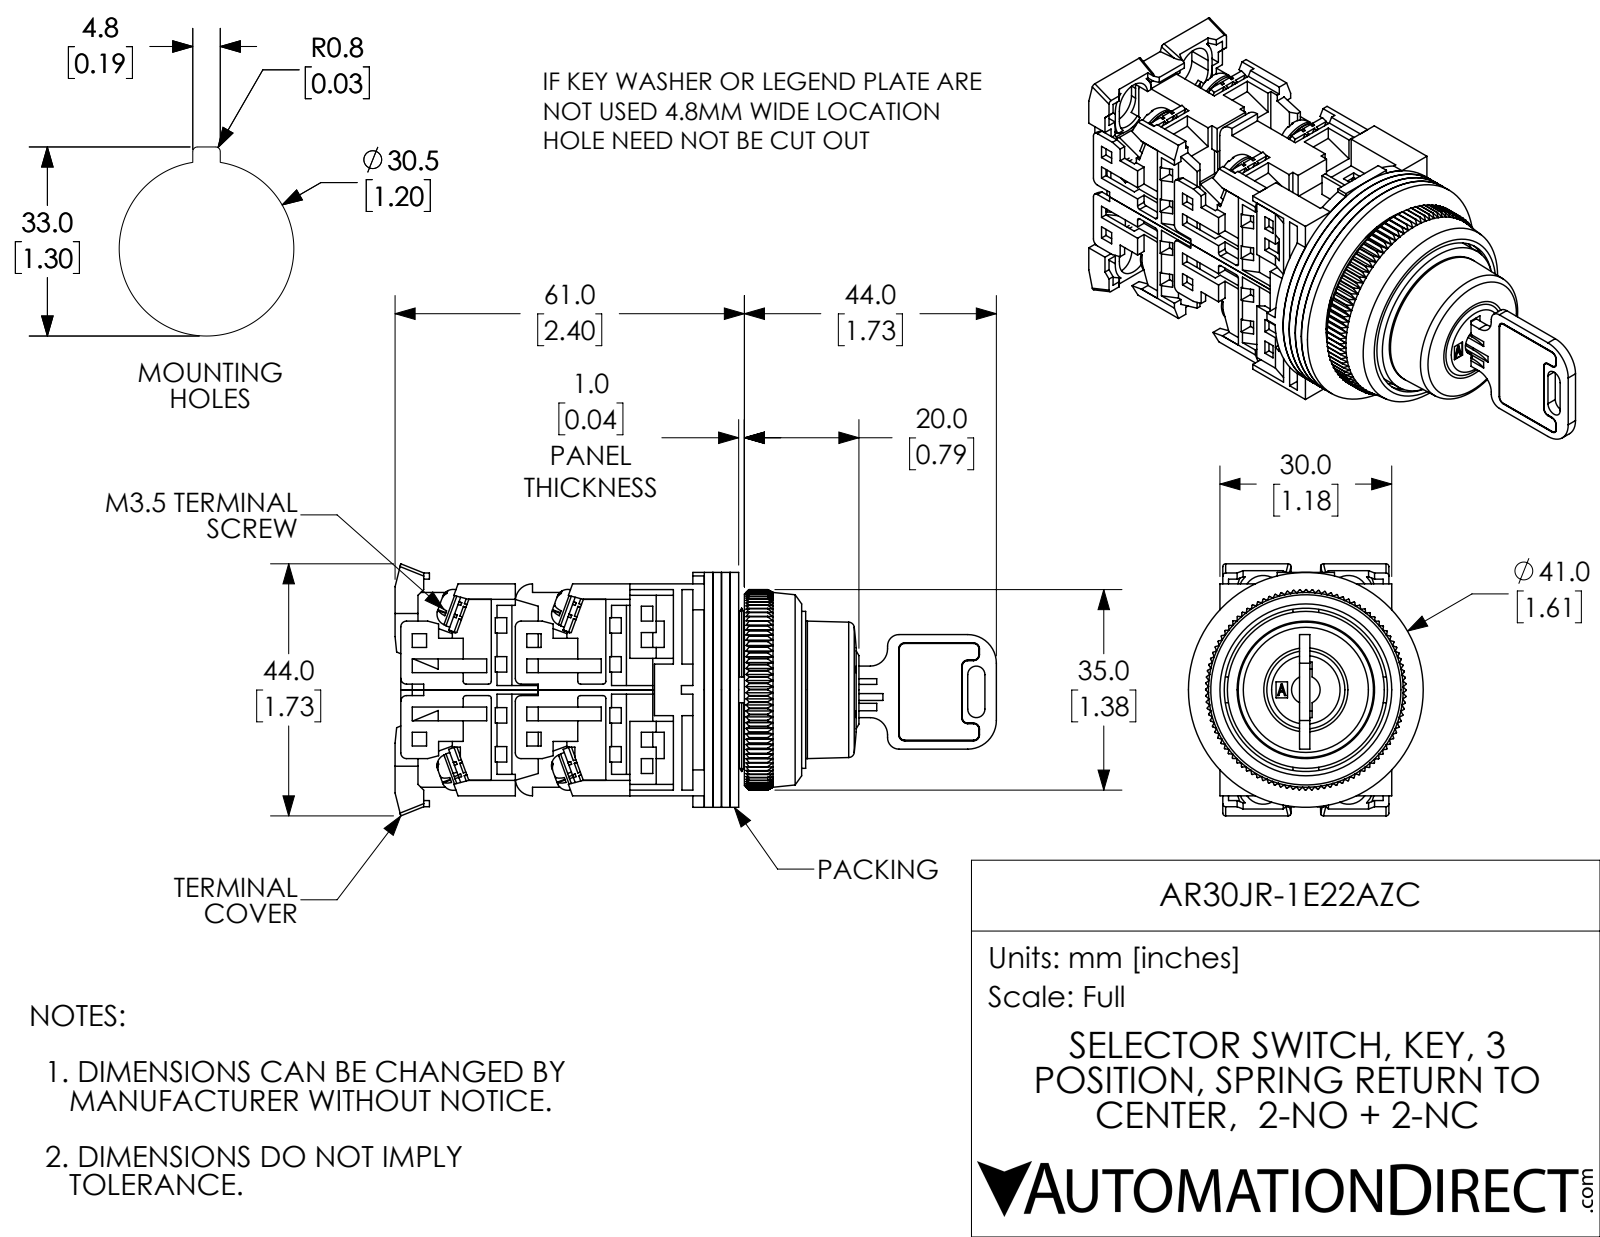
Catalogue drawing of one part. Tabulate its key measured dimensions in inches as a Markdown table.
| quantity | value |
| --- | --- |
| part name | AR30JR-1E22AZC |
| STEP written by | SolidWorks 2017 (AUTOMOTIVE_DESIGN) |
| units | inches |
| bodies | 38 solids, 2546 faces (1941 planar, 325 cylindrical, 280 other) |
| overall size | 4.134 × 1.732 × 1.614 |
| volume | 3.32 in³ |
| surface area | 69.28 in² |
| round holes (diameter × count) | 0.138 × 12, 0.142 × 8, 0.118 × 1, 0.709 × 1, 0.945 × 1, 1.122 × 1, 1.181 × 1, 1.252 × 1 |
| round bosses / shafts (diameter × count) | 0.26 × 8, 0.138 × 8, 1.614 × 1, 1.15 × 1, 1.079 × 1 |
| partial cylindrical surfaces (radius × count) | 0.059 × 34, 0.02 × 16, 0.039 × 9, 0.118 × 6, 0.008 × 4, 0.138 × 4, 0.177 × 4, 0.079 × 2 |
| main face-to-face distances | 0.059, 0.118, 0.039, 0.787, 0.079, 0.177, 0.063, 0.138, 0.02, 0.256 |
| hole center spacings | 0.579, 0.269, 0.638, 0.61 |
